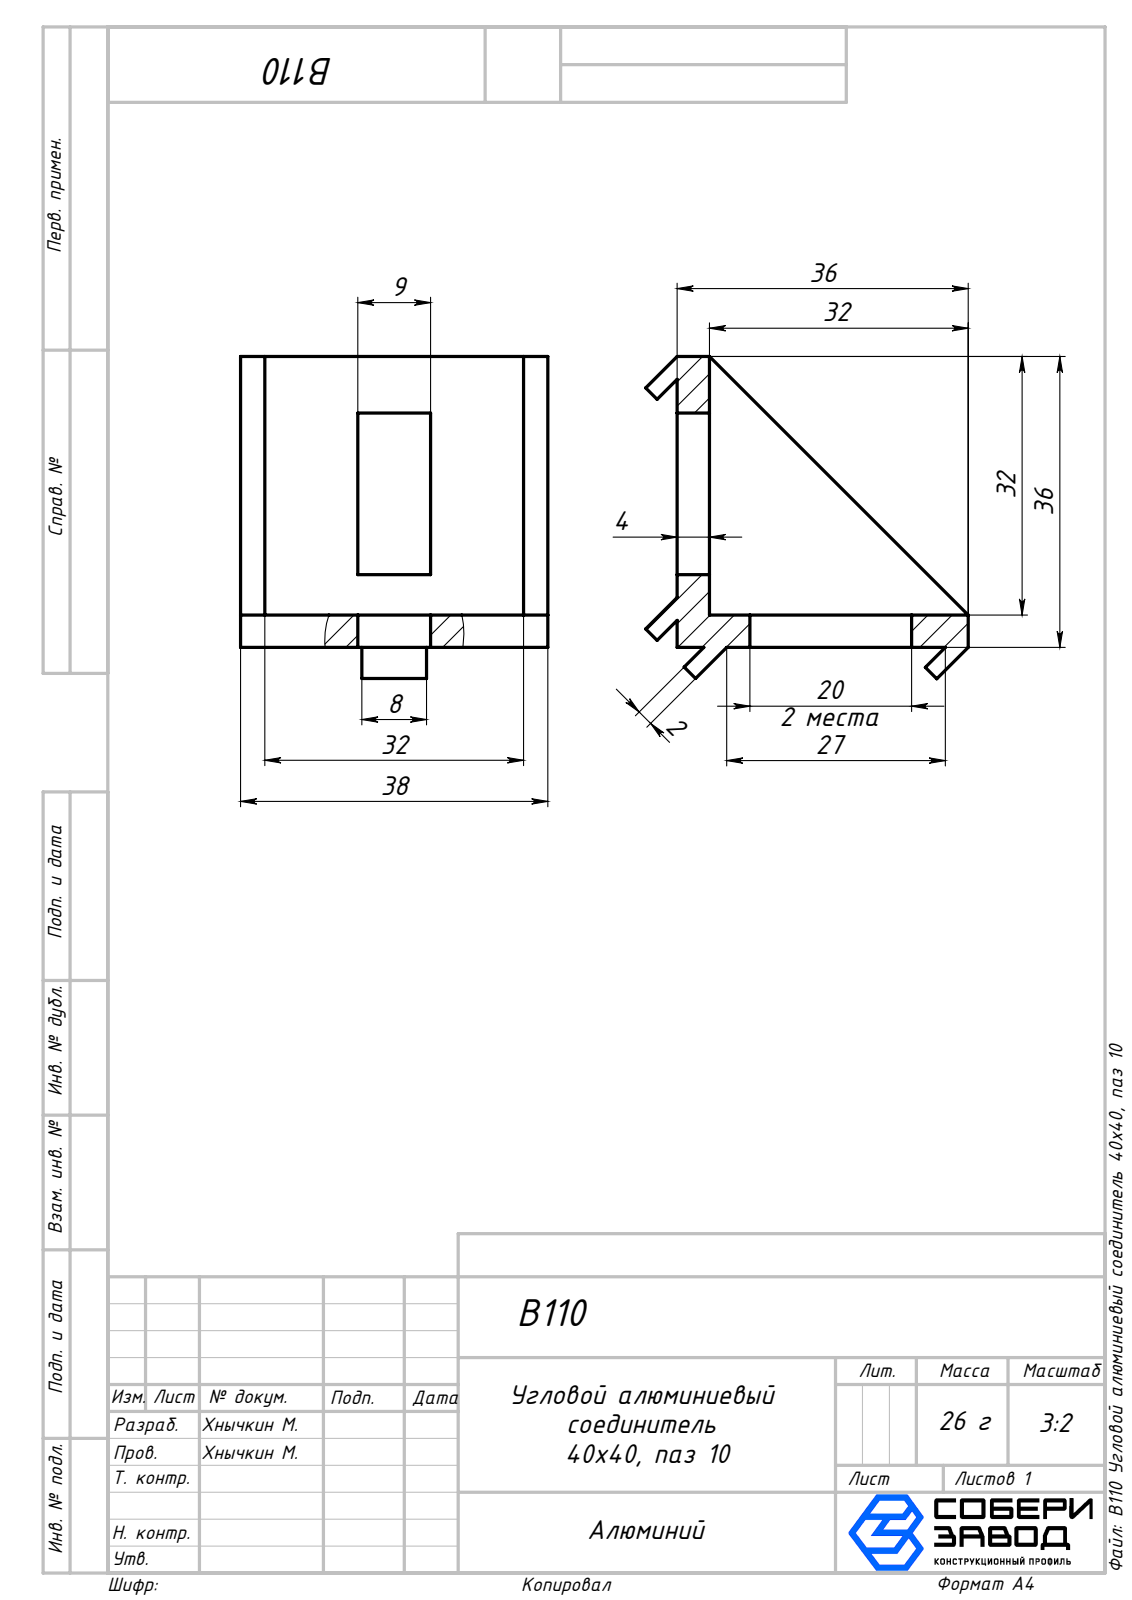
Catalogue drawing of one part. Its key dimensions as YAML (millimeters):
part_name: "B110 Угловой алюминиевый соединитель 40х40, паз 10"
step_written_by: "SolidWorks 2025 (AUTOMOTIVE_DESIGN)"
units: millimeters
bodies: {solids: 1, faces: 40, planar: 40, cylindrical: 0, other: 0}
overall_size: [39.89, 39.89, 38]
volume: 12255
surface_area: 8028
face_to_face_distances: [4, 3, 35, 32, 38, 14.5, 23.5, 11.5, 20.5, 36]
